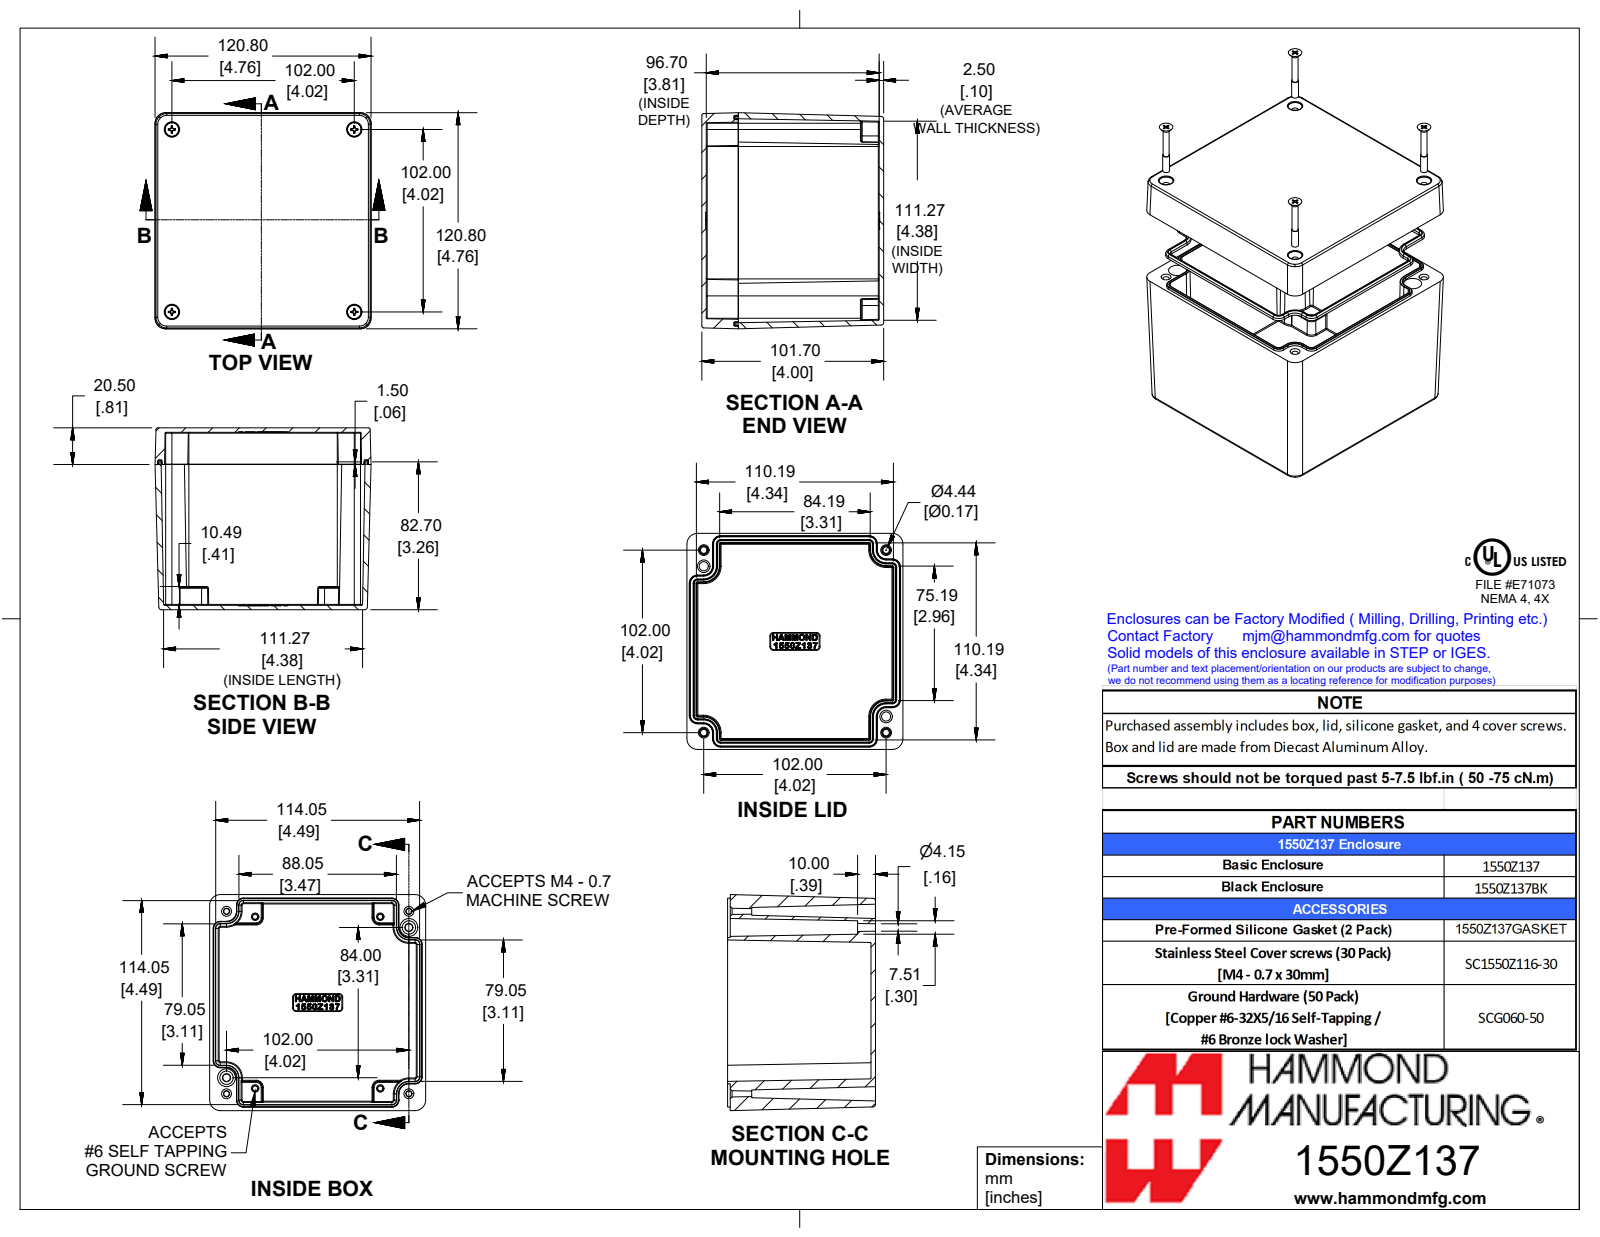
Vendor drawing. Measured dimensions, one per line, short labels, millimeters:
name: 1550Z137
written by: SolidWorks 2019 (AUTOMOTIVE_DESIGN)
unit: mm
bodies: 7 solids, 1434 faces (384 planar, 256 cylindrical, 794 other)
size: 120.8 × 120.8 × 101.7
volume: 291 000 mm³; area: 165 400 mm²
holes: 4× ⌀3.6
bosses: 4× ⌀7.6, 4× ⌀3.9, 4× ⌀3.3
rounds: 50× R0.2, 46× R0.5, 24× R1, 20× R0.3, 8× R6, 4× R1.5
face distances: 2.5, 99.2, 101.7, 96.7, 120.8, 112.1, 81.2, 18, 13, 99.1
hole spacings: 102, 144.2
